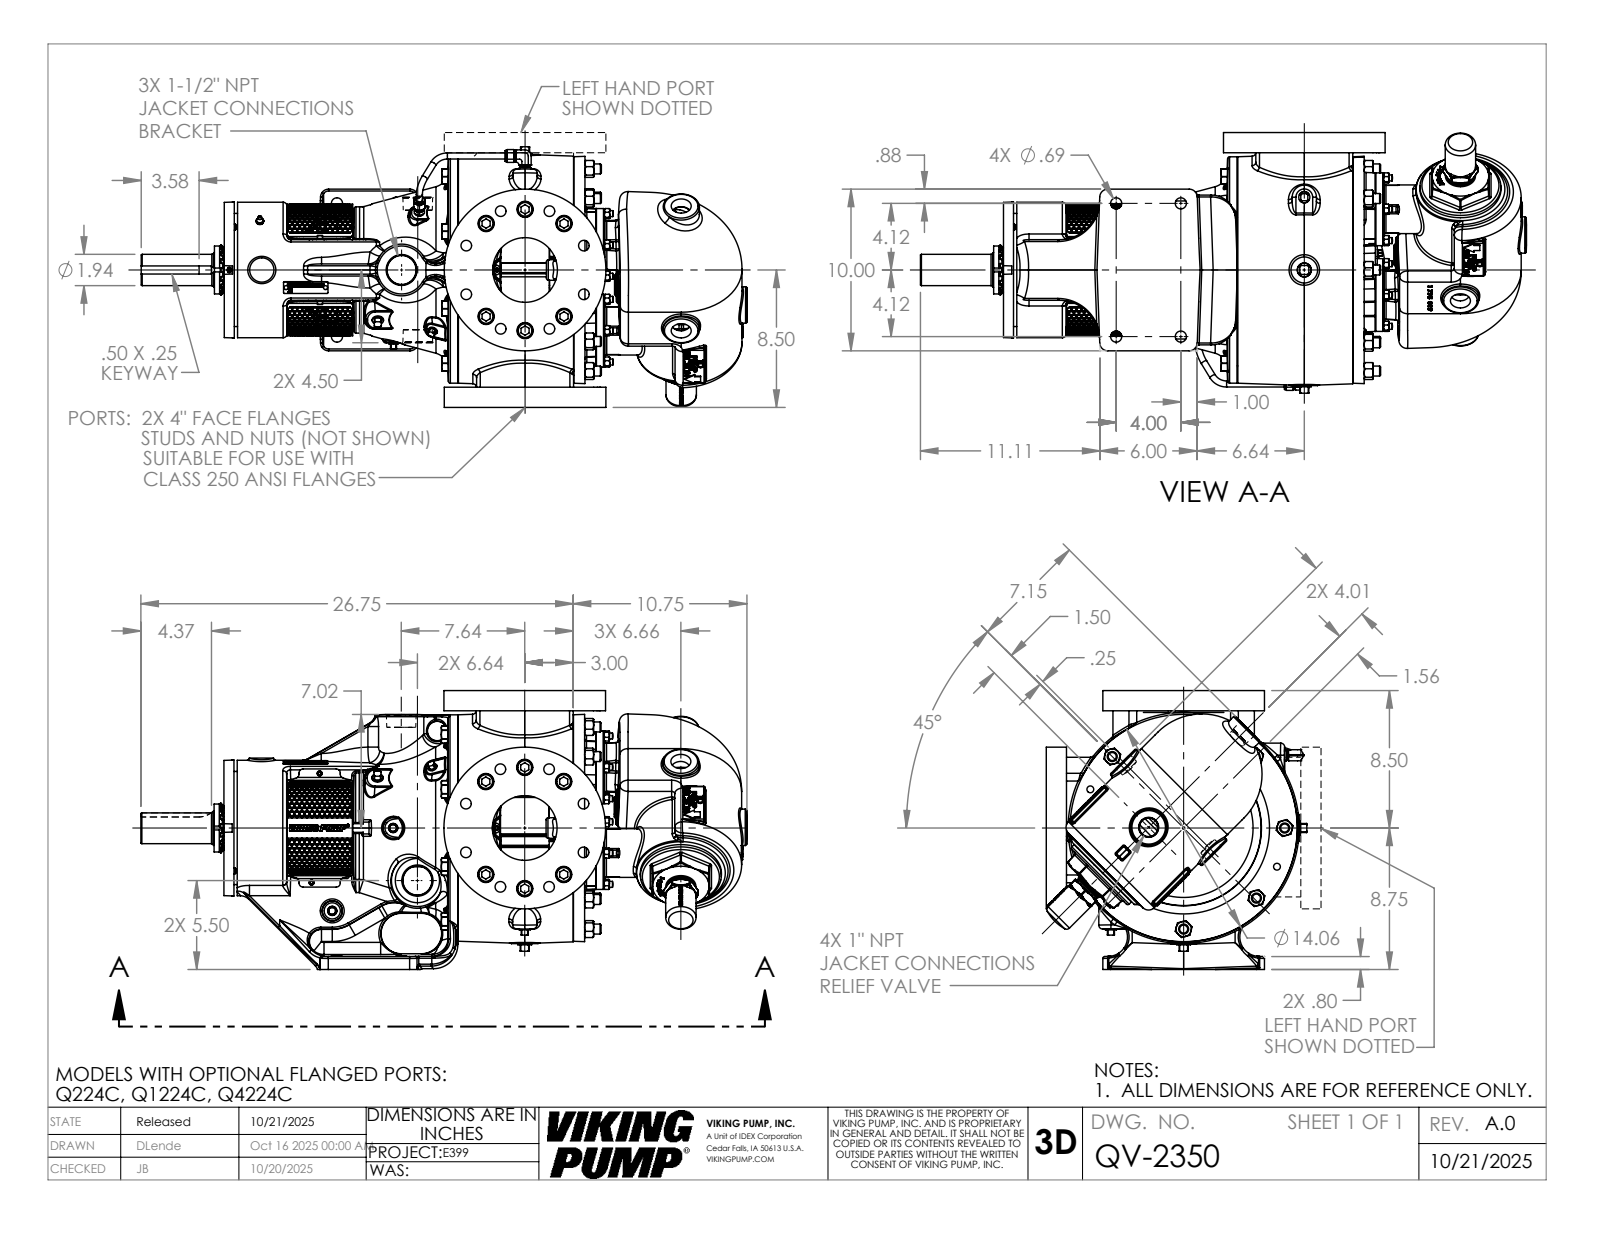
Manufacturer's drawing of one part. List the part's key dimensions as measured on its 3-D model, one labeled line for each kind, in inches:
Part name (STEP PRODUCT): QV-2350
STEP written by: SolidWorks 2024 (AUTOMOTIVE_DESIGN)
Units: inches
Bodies: 1 solid, 5105 faces (1677 planar, 768 cylindrical, 2660 other)
Overall size (bounding box): 37.499 × 17.25 × 16.221
Volume: 2 915 in³ · Surface area: 2 635 in²
Round holes (diameter × count): ⌀0.656 ×16, ⌀1 ×13, ⌀0.25 ×9, ⌀0.266 ×8, ⌀1.157 ×8, ⌀0.688 ×4, ⌀0.159 ×2, ⌀0.313 ×2, ⌀0.422 ×2, ⌀4 ×2, ⌀0.453 ×1, ⌀1.435 ×1
Round bosses / shafts (diameter × count): ⌀0.937 ×12, ⌀0.617 ×8, ⌀0.369 ×8, ⌀0.375 ×4, ⌀0.312 ×3, ⌀0.19 ×3, ⌀10 ×2, ⌀4.5 ×2
Partial cylindrical surfaces — rounded edges, fillets, slot ends (radius × count): R0.12 ×60, R0.5 ×28, R0.06 ×26, R0.75 ×24, R0.015 ×18, R0.092 ×18, R0.07 ×16, R0.19 ×16
Main face-to-face distances: 1.25, 17.25, 22.317, 16, 3.82, 18.498, 1.5, 7.972, 4.153, 14.345
Hole centre spacings: 3.75, 7.276, 2.079, 3.937, 5.783, 3.014, 1.184, 2.713
